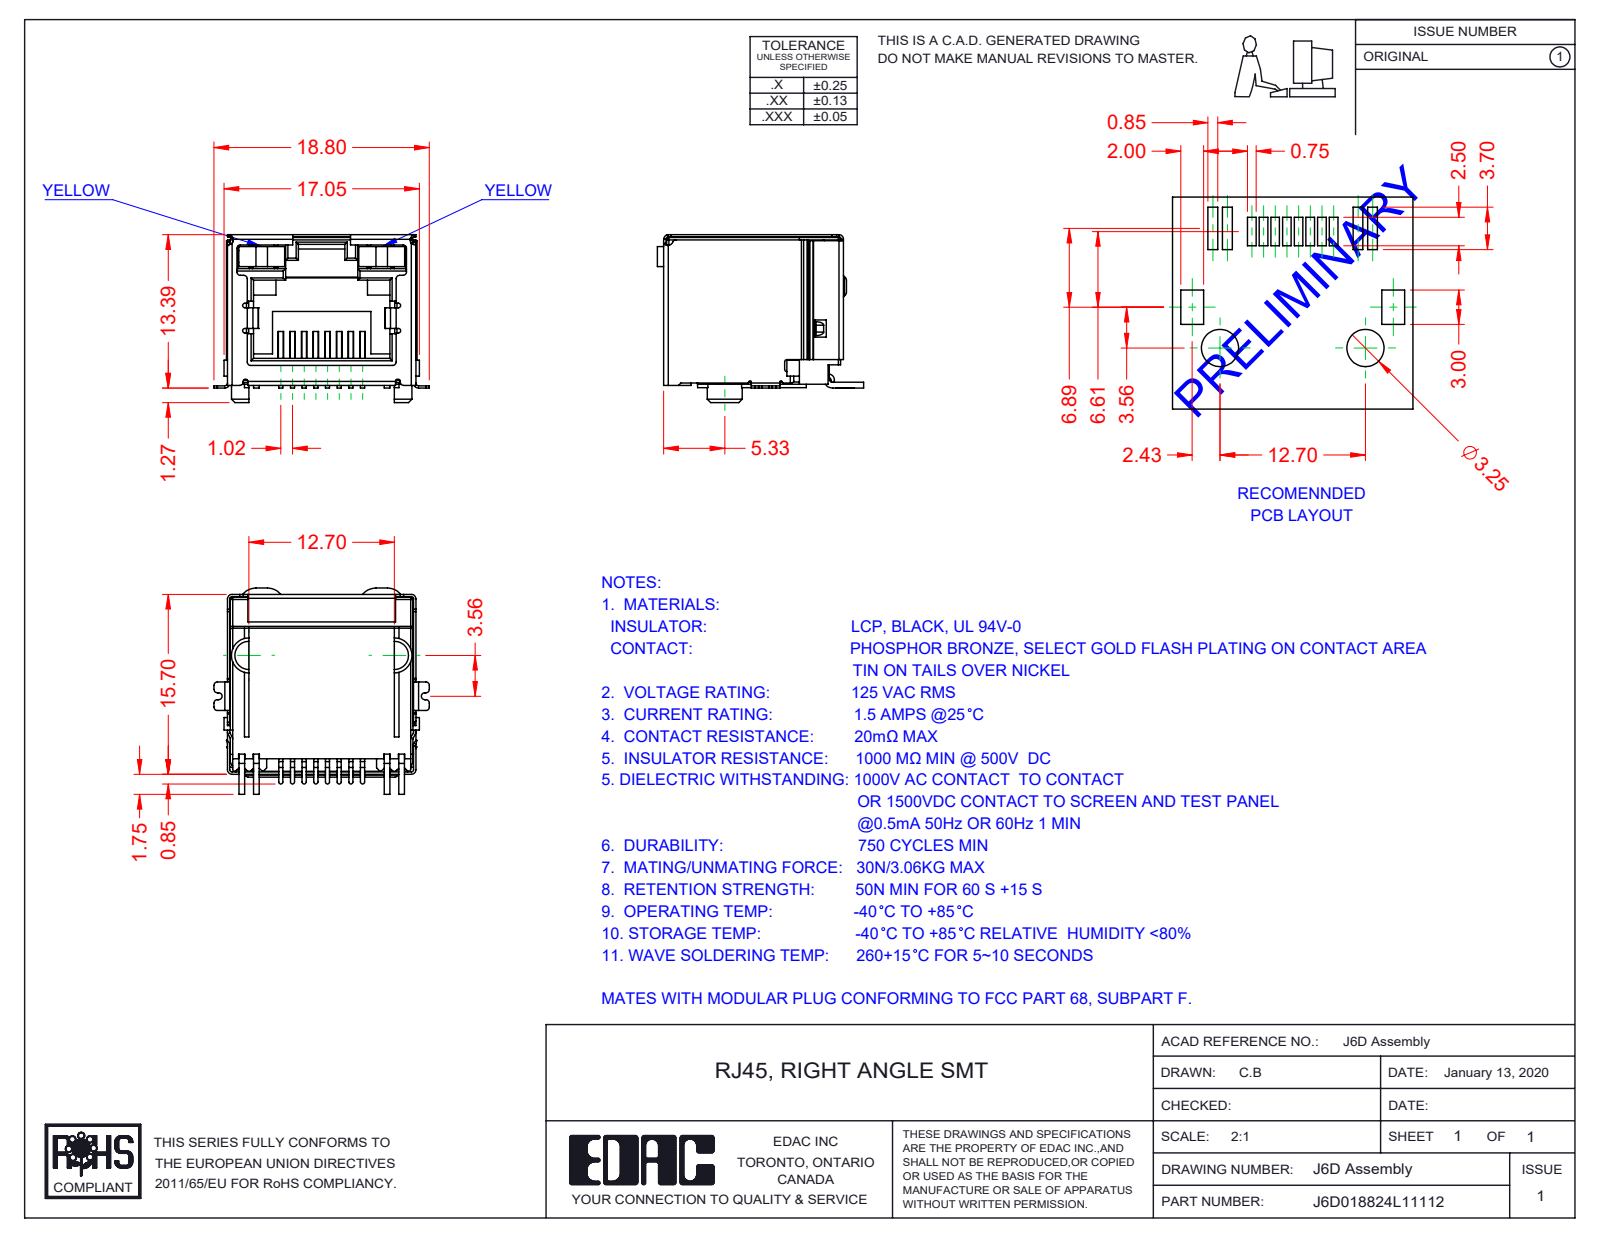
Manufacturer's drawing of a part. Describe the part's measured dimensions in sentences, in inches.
The part is named "6D Shield_LED - No EMI; J6D018824L11112; 6D LED RH_1-Yellow; 6D LED LH_1-Yellow (+2 more)". Its 3-D file was written by "SolidWorks 2016 (CONFIG_CONTROL_DESIGN)". It is 12 solids with 893 faces: 644 planar, 216 cylindrical and 33 other. Overall it measures 0.74 by 0.709 by 0.577 inches. Its volume is 0.11 cubic inches and its surface area 7.592 square inches. Partial cylindrical surfaces (rounded edges, fillets, slot ends): 39 of radius 0.012, 37 of radius 0.008, 16 of radius 0.016, 12 of radius 0.004, 8 of radius 0.006, 8 of radius 0.007, 6 of radius 0.02, 5 of radius 0.059. The main face-to-face distances are 0.63, 0.64, 0.638, 0.089, 0.039, 0.628, 0.632, 0.504, 0.018, 0.648.
